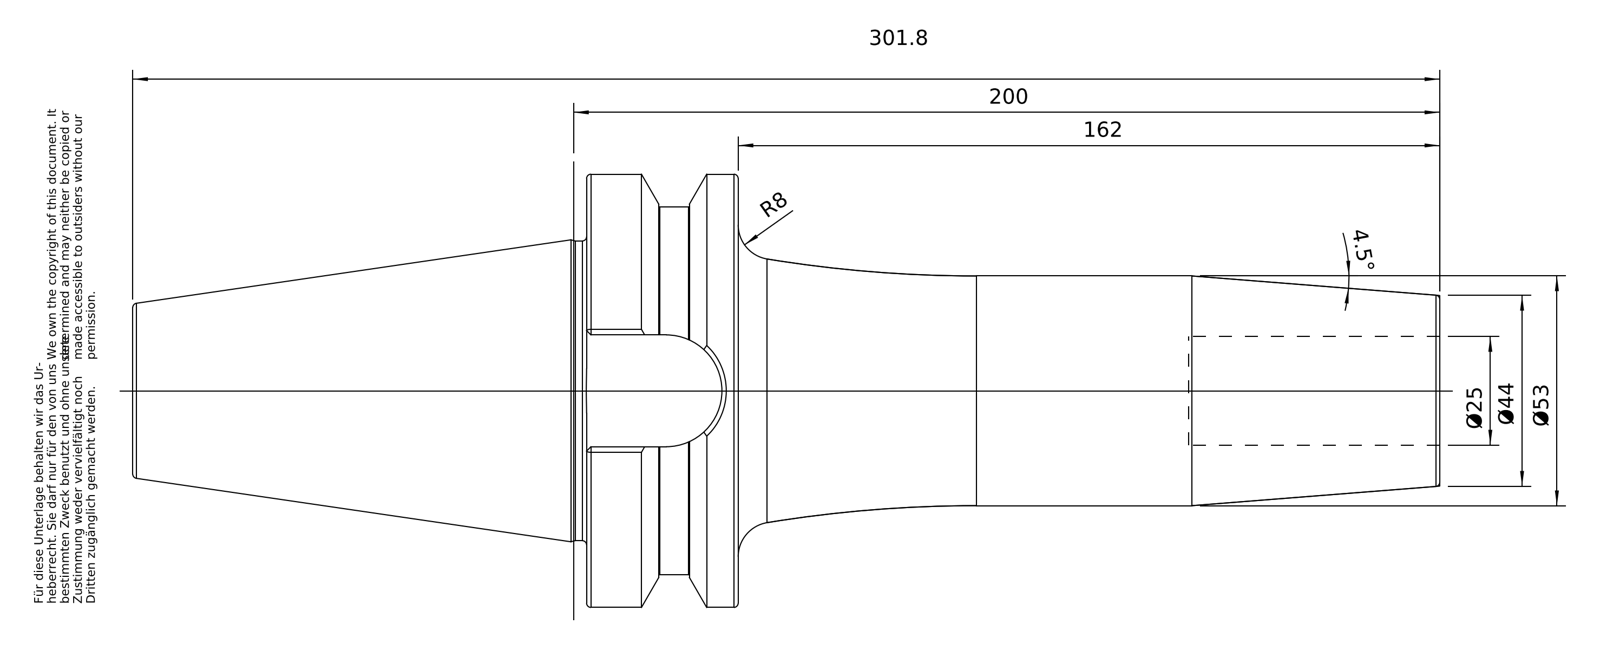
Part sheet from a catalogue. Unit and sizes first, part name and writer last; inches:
Units: inches
Overall size (bounding box): 11.882 × 3.936 × 3.936
Round holes (diameter × count): ⌀0.817 ×1, ⌀0.984 ×1, ⌀0.985 ×1, ⌀1.012 ×1
Round bosses / shafts (diameter × count): ⌀3.936 ×1, ⌀3.337 ×1, ⌀2.722 ×1, ⌀2.087 ×1, ⌀0.945 ×1
Partial cylindrical surfaces — rounded edges, fillets, slot ends (radius × count): R0.508 ×1
Main face-to-face distances: 1.378, 7.756, 6.378, 2.772, 4.126, 5.504, 11.882, 9.598, 5.472, 4.094
Volume: 48.51 in³ · Surface area: 125.8 in²
Bodies: 1 solid, 98 faces (26 planar, 22 cylindrical, 50 other)
Part name (STEP PRODUCT): 50-646-25
STEP written by: PRO/ENGINEER BY PARAMETRIC TECHNOLOGY CORPORATION, 2010430 (CONFIG_CONTROL_DESIGN)
